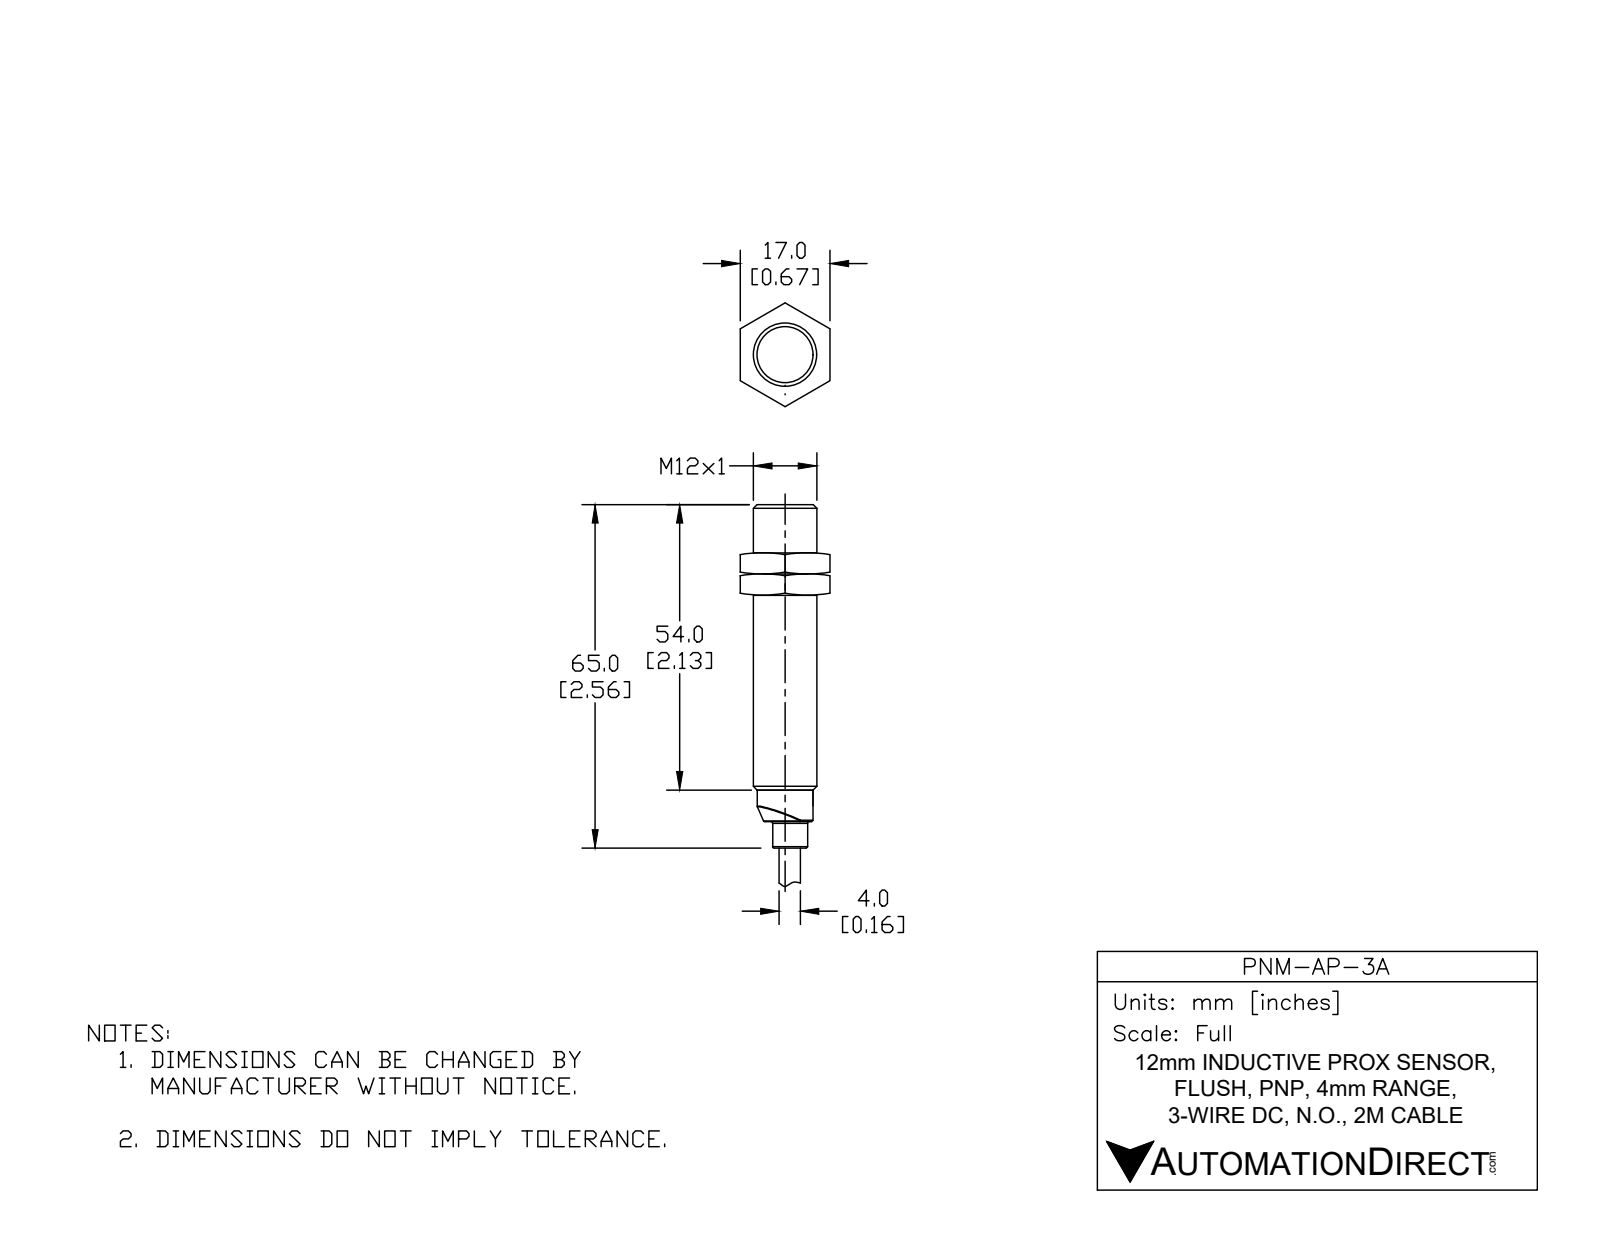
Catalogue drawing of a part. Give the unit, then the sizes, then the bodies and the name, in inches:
Units: inches
Overall size (bounding box): 4.559 × 0.472 × 0.472
Round holes (diameter × count): ⌀0.161 ×1, ⌀0.401 ×1
Round bosses / shafts (diameter × count): ⌀0.472 ×1, ⌀0.417 ×1, ⌀0.415 ×1, ⌀0.384 ×1, ⌀0.26 ×1, ⌀0.157 ×1
Partial cylindrical surfaces — rounded edges, fillets, slot ends (radius × count): R0.091 ×1
Main face-to-face distances: 2.362, 2.559, 0.197, 4.559, 2.197, 2, 0.022, 2.34, 2.537, 4.537
Hole centre spacings: 0.039
Volume: 0.452 in³ · Surface area: 4.972 in²
Bodies: 1 solid, 68 faces (21 planar, 19 cylindrical, 28 other)
Part name (STEP PRODUCT): PNM-AP-3A
STEP written by: SolidWorks 2017 (AUTOMOTIVE_DESIGN)
